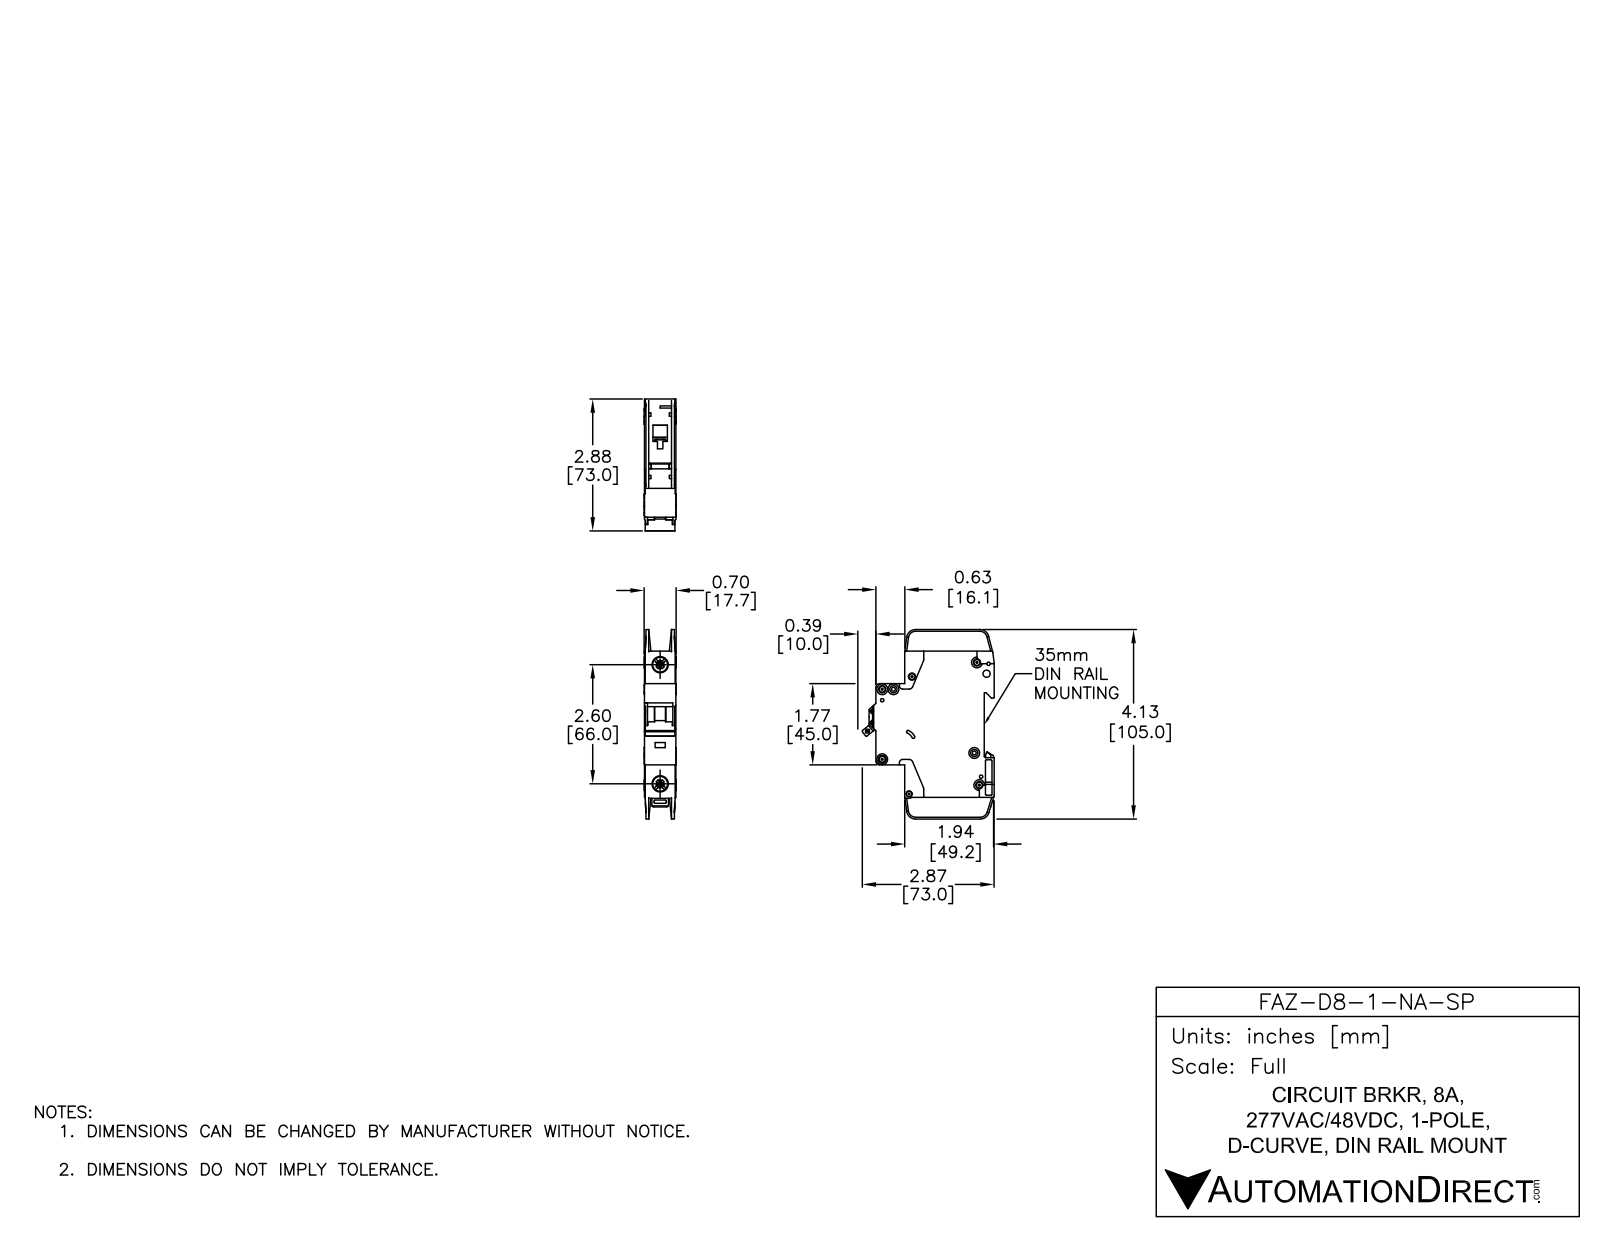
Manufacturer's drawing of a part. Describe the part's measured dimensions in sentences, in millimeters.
The part is named "FAZ-D8-1-NA-SP". Its 3-D file was written by "SolidWorks 2014 (AUTOMOTIVE_DESIGN)". It is 3 solids with 784 faces: 409 planar, 263 cylindrical and 112 other. Overall it measures 105 by 73.04 by 17.7 millimeters. Its volume is 77 695 cubic millimeters and its surface area 24 740 square millimeters. Round holes: 7 of diameter 3.6, 2 of diameter 1.09, 2 of diameter 1.5, 2 of diameter 4, 2 of diameter 7.15, 2 of diameter 8.2, 1 of diameter 1.9, 1 of diameter 2.15, 1 of diameter 2.2, 1 of diameter 2.55, 1 of diameter 3.3, 1 of diameter 3.4. Round bosses or shafts: 7 of diameter 6, 1 of diameter 2.5. Partial cylindrical surfaces (rounded edges, fillets, slot ends): 29 of radius 0.25, 18 of radius 0.5, 10 of radius 1, 10 of radius 2, 5 of radius 5, 4 of radius 4, 3 of radius 1.8, 2 of radius 0.2. The main face-to-face distances are 17.5, 15.05, 0.7, 2.45, 1.75, 15.75, 13.3, 14, 12.6, 2. The hole center spacings are 6.2, 5.19, 6.1, 8.19, 8.56, 8.7, 11.11, 12.45.
